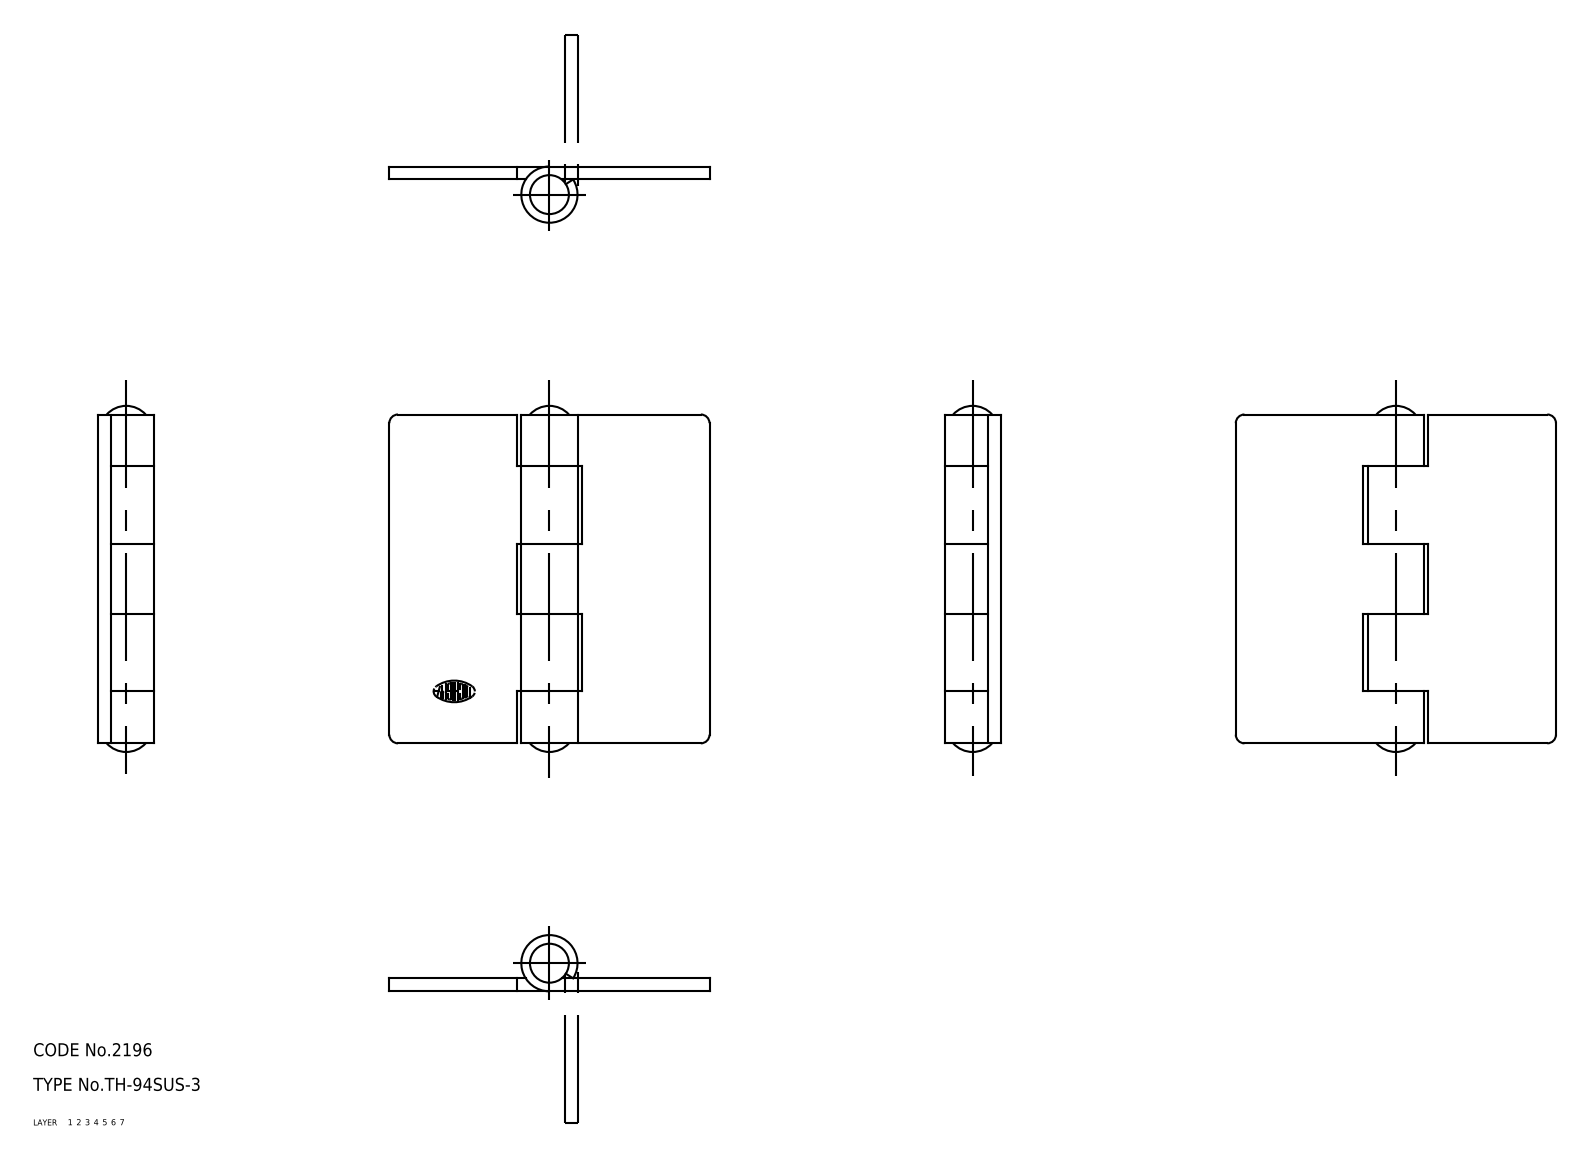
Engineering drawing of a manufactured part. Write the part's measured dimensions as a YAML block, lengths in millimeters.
part_name: "hinge piece_B; hinge piece_A; shaft; TH_94SUS_3_19339_36"
step_written_by: "CADfix (AUTOMOTIVE_DESIGN)"
units: millimeters
bodies: {solids: 3, faces: 48, planar: 0, cylindrical: 0, other: 48}
overall_size: [79.98, 74, 13]
volume: 24228
surface_area: 18255
